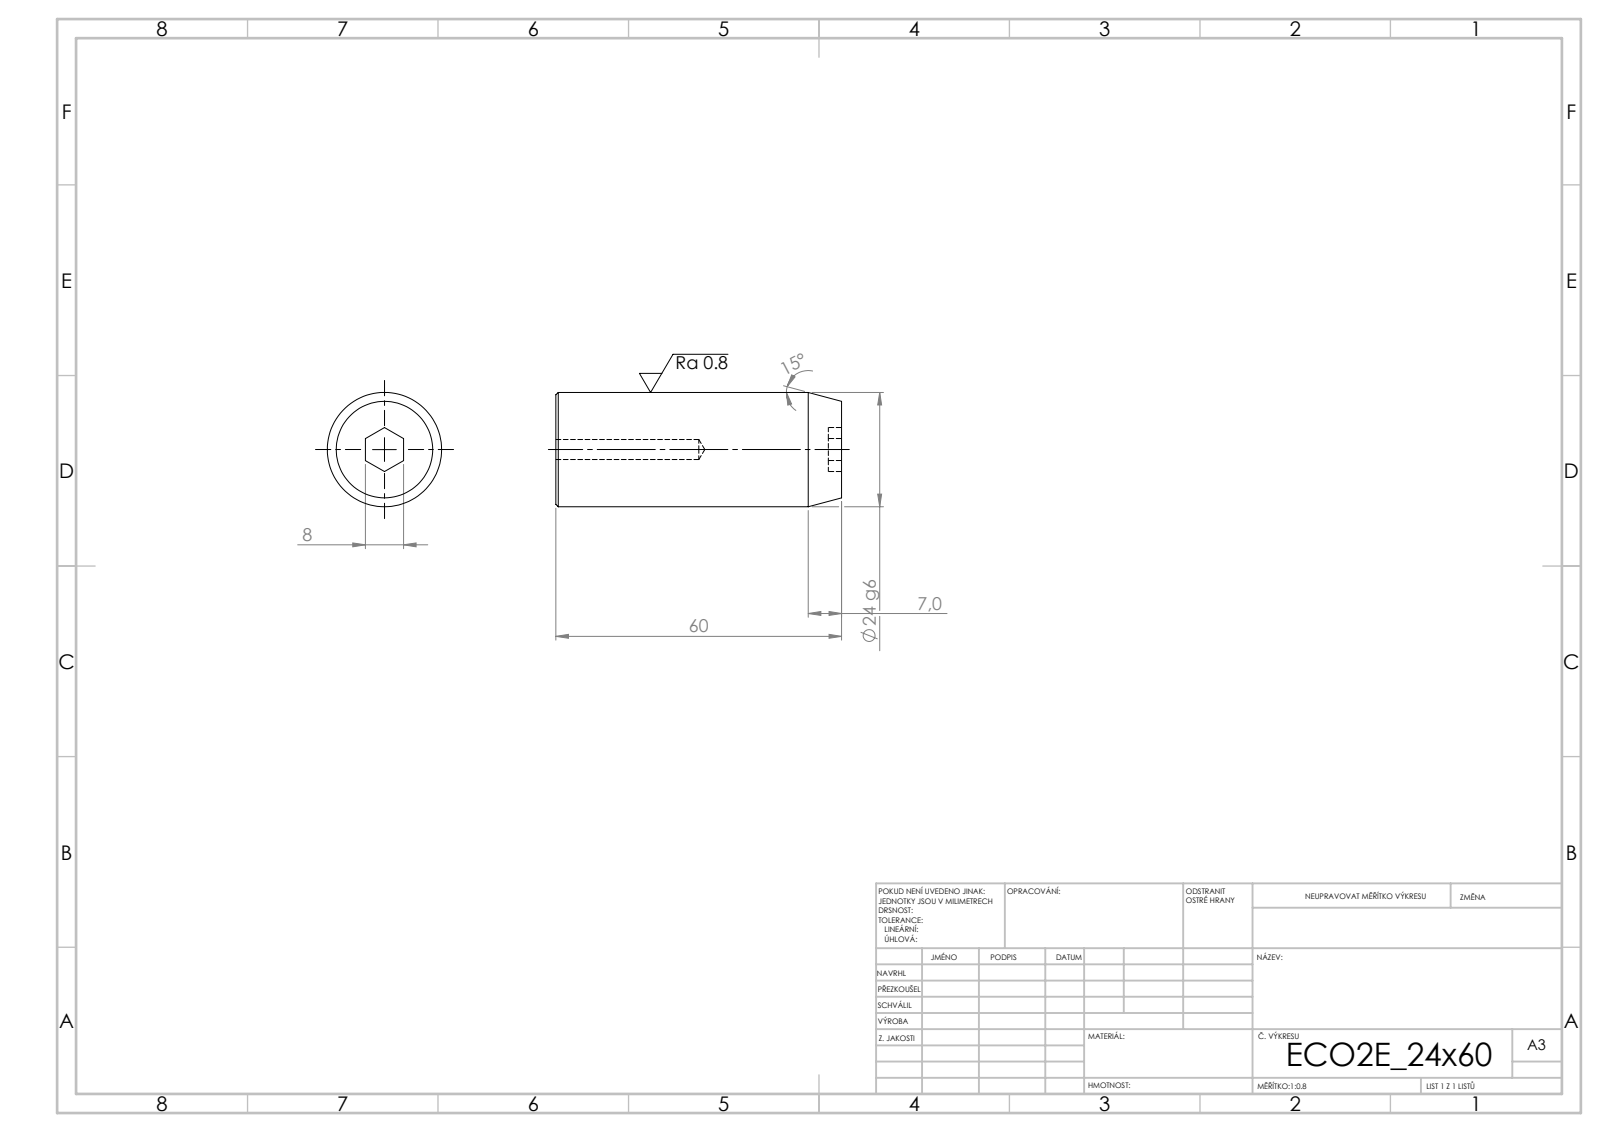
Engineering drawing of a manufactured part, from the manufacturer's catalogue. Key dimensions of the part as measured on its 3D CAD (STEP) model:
STEP written by: SolidWorks 2019 (CONFIG_CONTROL_DESIGN)
Units: millimetres
Bodies: 1 solid, 19 faces (9 planar, 4 cylindrical, 6 other)
Overall size (bounding box): 60 × 24 × 24
Volume: 26 088 mm³ · Surface area: 5 728 mm²
Round holes (diameter × count): ⌀4.2 ×1
Round bosses / shafts (diameter × count): ⌀24 ×1
Main face-to-face distances: 60, 2.8, 57.2, 8
